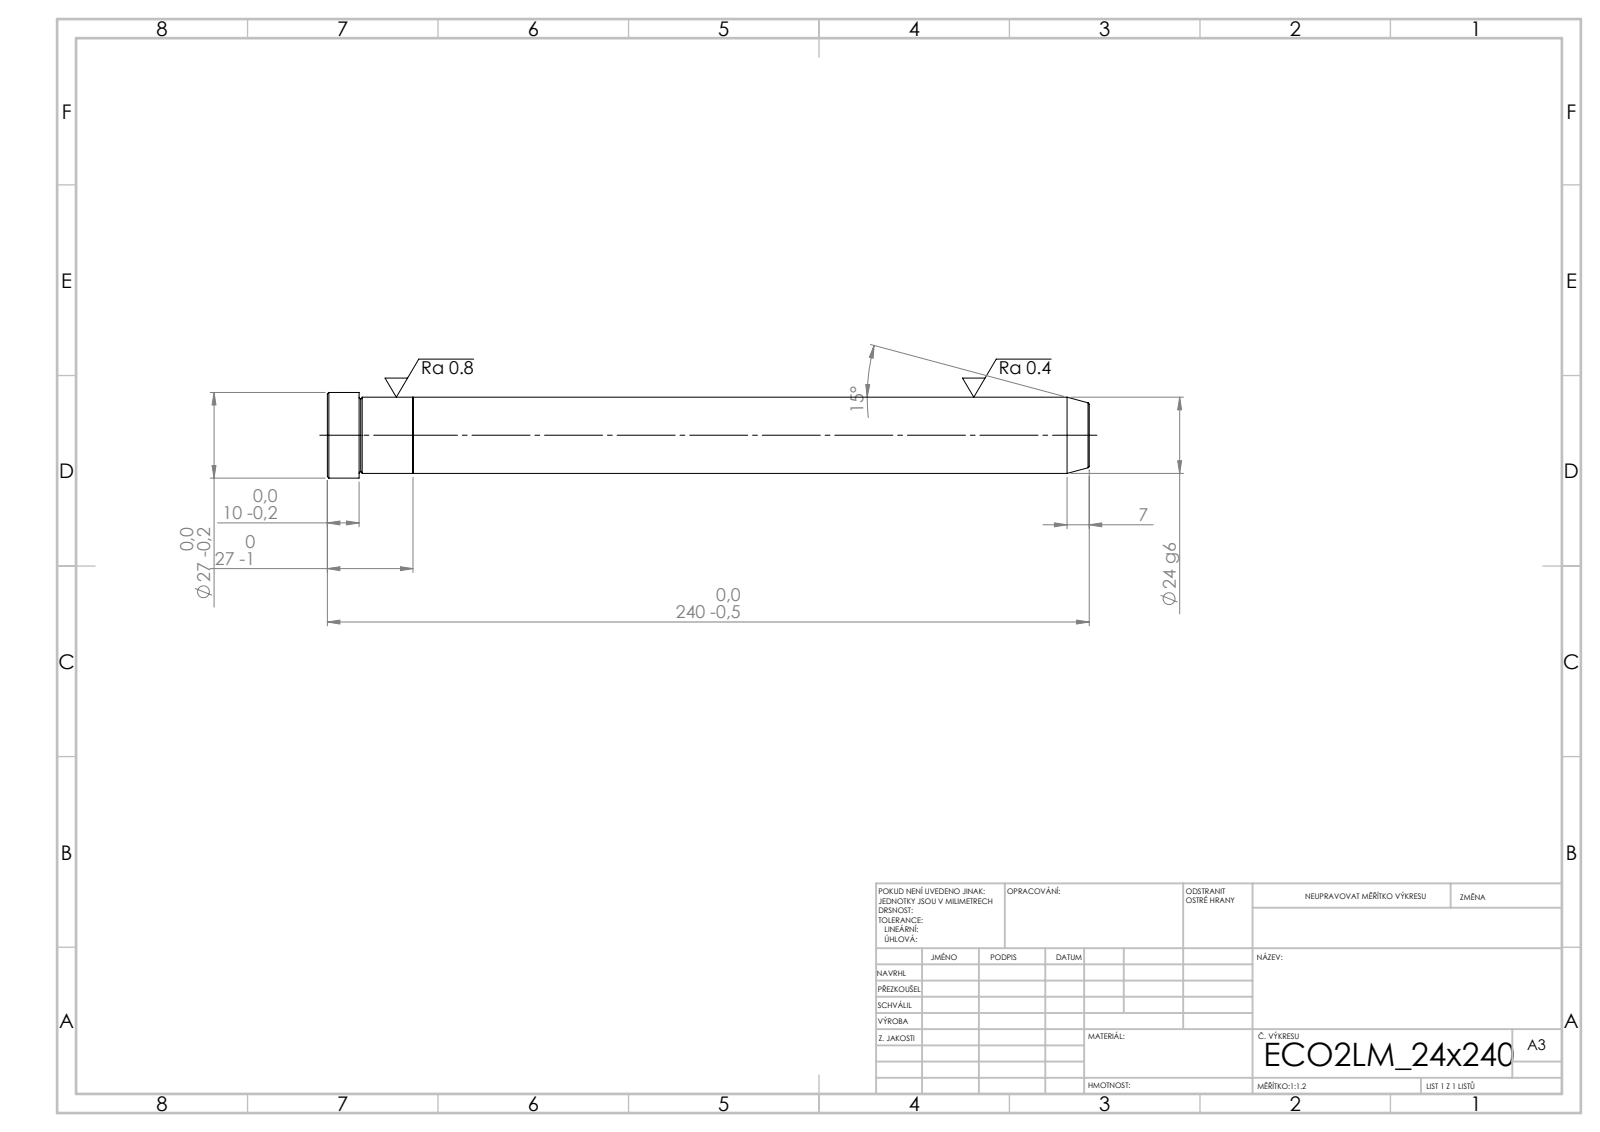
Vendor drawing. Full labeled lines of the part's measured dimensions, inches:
STEP written by: SolidWorks 2019 (CONFIG_CONTROL_DESIGN)
Units: inches
Bodies: 2 solids, 21 faces (5 planar, 6 cylindrical, 10 other)
Overall size (bounding box): 9.449 × 1.063 × 1.063
Volume: 6.668 in³ · Surface area: 31.14 in²
Round bosses / shafts (diameter × count): ⌀1.063 ×1, ⌀0.945 ×1
Main face-to-face distances: 1.063, 8.386, 9.449, 9.055, 0.669, 0.394
